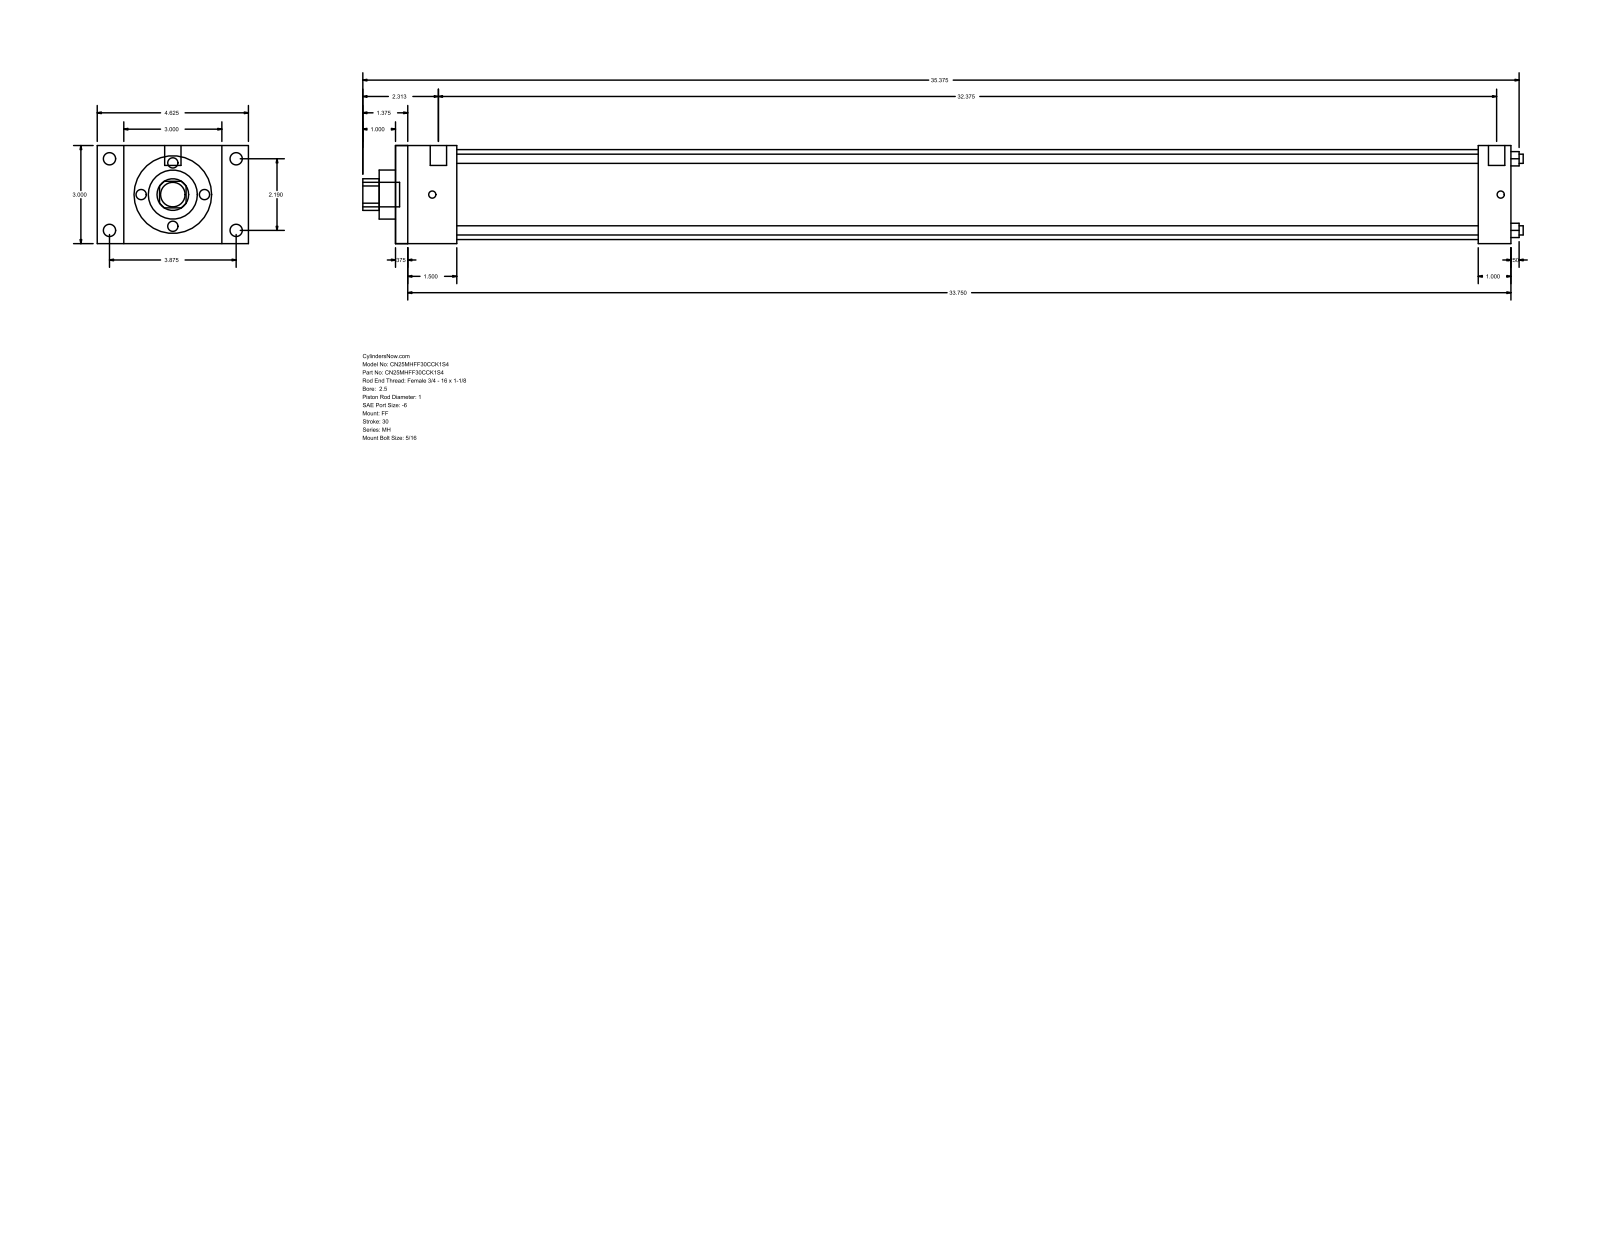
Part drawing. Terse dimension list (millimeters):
name: MH_FF__0250_1
written by: GSSL Pune (CONFIG_CONTROL_DESIGN)
unit: mm
bodies: 0 solids, 92 faces (64 planar, 28 cylindrical, 0 other)
size: 901.7 × 117.47 × 76.2
holes: 4× ⌀7.14, 1× ⌀25.4, 1× ⌀38.1, 1× ⌀69.85
bosses: 4× ⌀9.53, 4× ⌀5.56, 2× ⌀12.7, 1× ⌀19.05
rounds: 1× R12.29
face distances: 76.2, 866.77, 9.52, 857.25, 25.4, 47.63, 841.37, 38.11, 831.85, 793.74
hole spacings: 39.33, 55.62, 78.66
